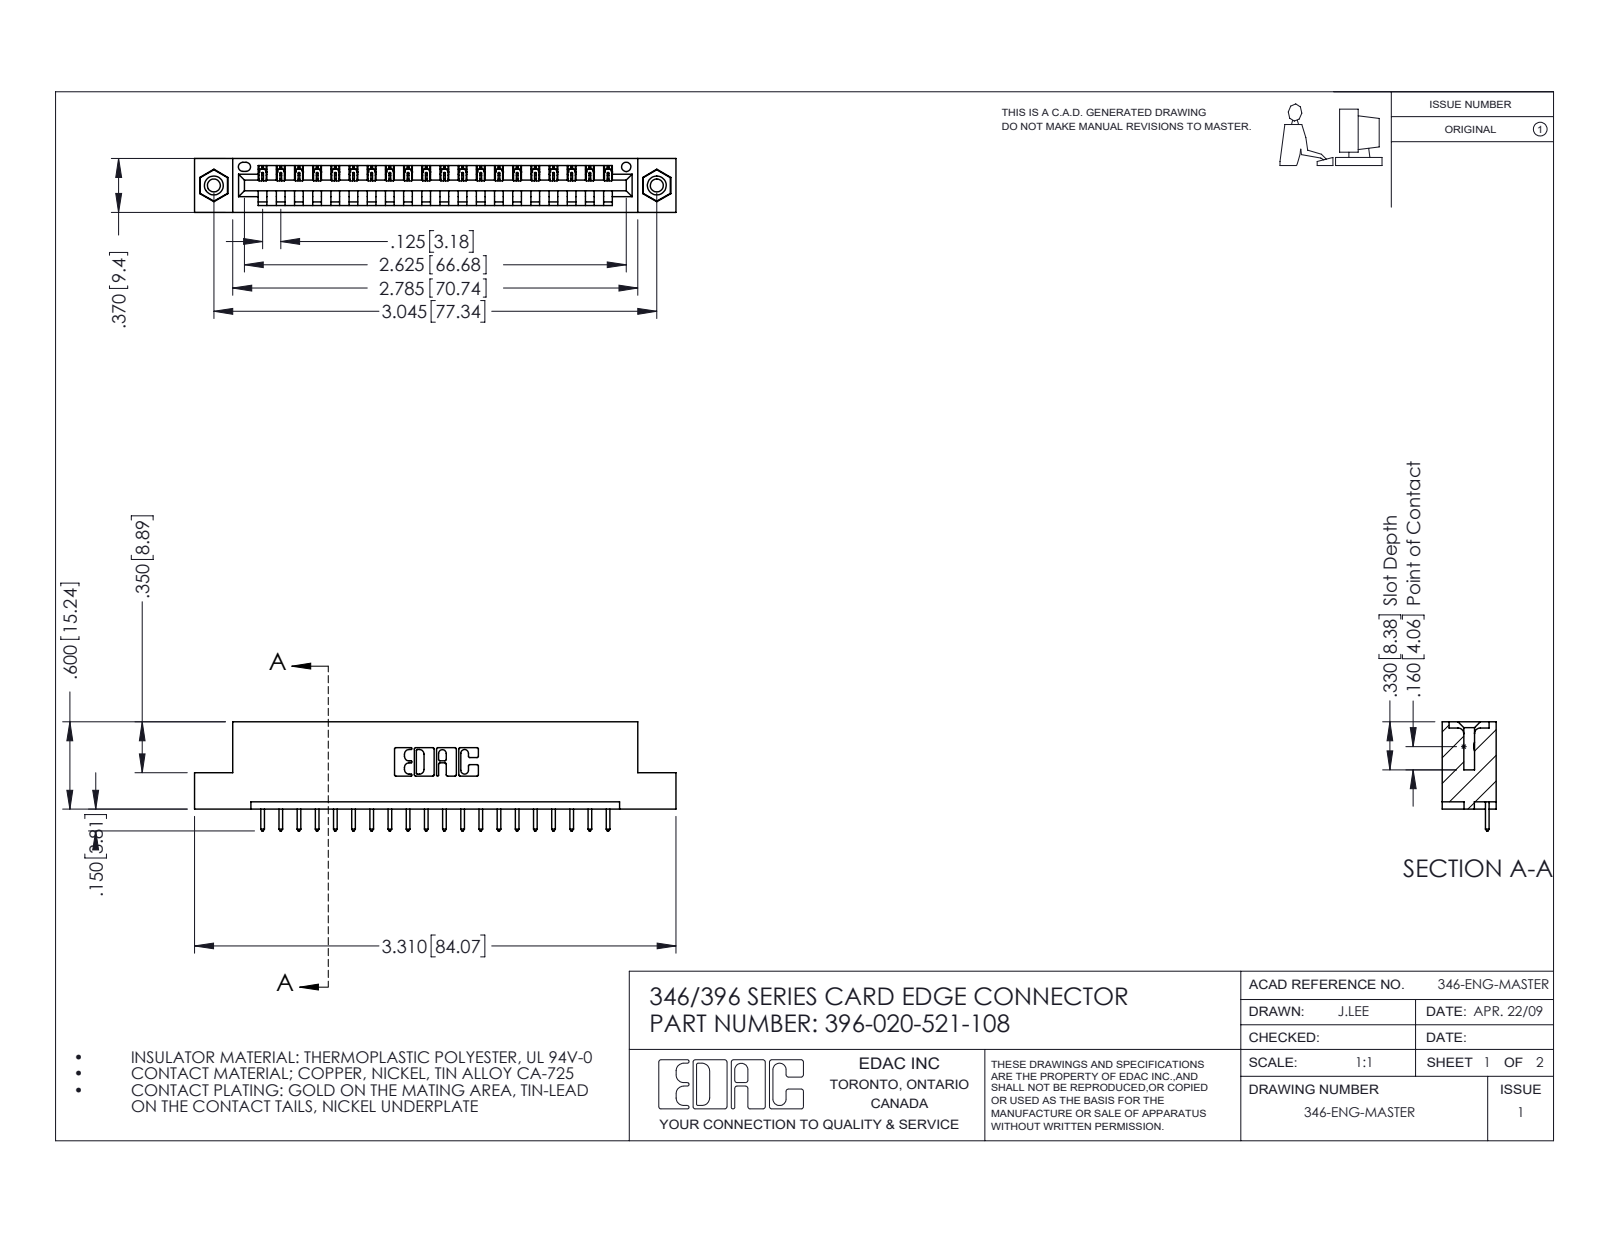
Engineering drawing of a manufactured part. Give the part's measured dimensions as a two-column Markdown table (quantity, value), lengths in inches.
| quantity | value |
| --- | --- |
| part name | 346 Part_Flush Mounting Lugs - 0.156 Dia-TI; 345-250-001_345-250-003-102; 345-292-001_345-293-121; 396-020-521-108 |
| STEP written by | SolidWorks 2016 (CONFIG_CONTROL_DESIGN) |
| units | inches |
| bodies | 23 solids, 1342 faces (908 planar, 418 cylindrical, 16 other) |
| overall size | 3.31 × 0.75 × 0.37 |
| volume | 0.478 in³ |
| surface area | 14.49 in² |
| round holes (diameter × count) | 0.089 × 2, 0.125 × 2, 0.156 × 2, 0.064 × 1 |
| round bosses / shafts (diameter × count) | 0.155 × 2 |
| partial cylindrical surfaces (radius × count) | 0.006 × 40, 0.01 × 40, 0.01 × 22, 0.007 × 6, 0.031 × 6, 0.026 × 3, 0.031 × 2, 0.04 × 2 |
| main face-to-face distances | 0.048, 0.322, 0.37, 0.25, 0.072, 0.298, 0.025, 0.148, 0.222, 0.1 |
| hole center spacings | 0.246, 2.837, 3.045 |
